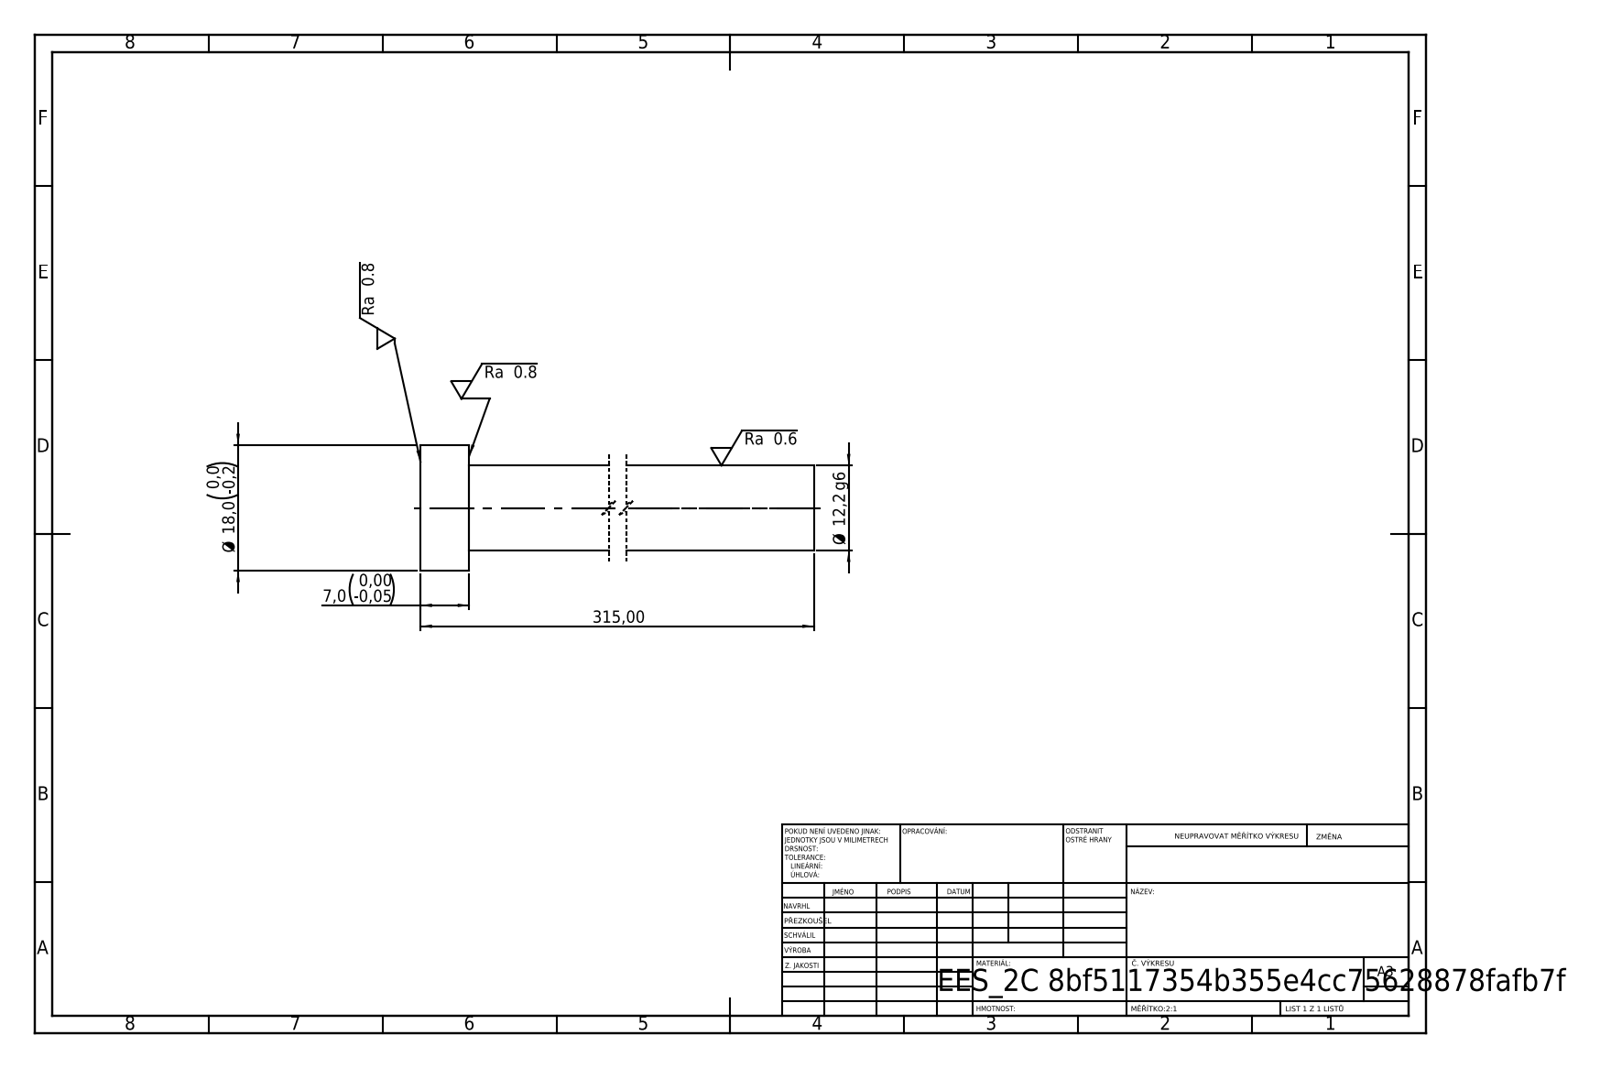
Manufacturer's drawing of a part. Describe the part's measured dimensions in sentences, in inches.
Its 3-D file was written by "SolidWorks 2019 (CONFIG_CONTROL_DESIGN)". It is 1 solid with 7 faces: 3 planar, 4 cylindrical and 0 other. Overall it measures 12.402 by 0.709 by 0.709 inches. Its volume is 2.306 cubic inches and its surface area 19.7 square inches. Round bosses or shafts: 1 of diameter 0.709, 1 of diameter 0.48. The main face-to-face distances are 0.276, 12.402, 12.126.
